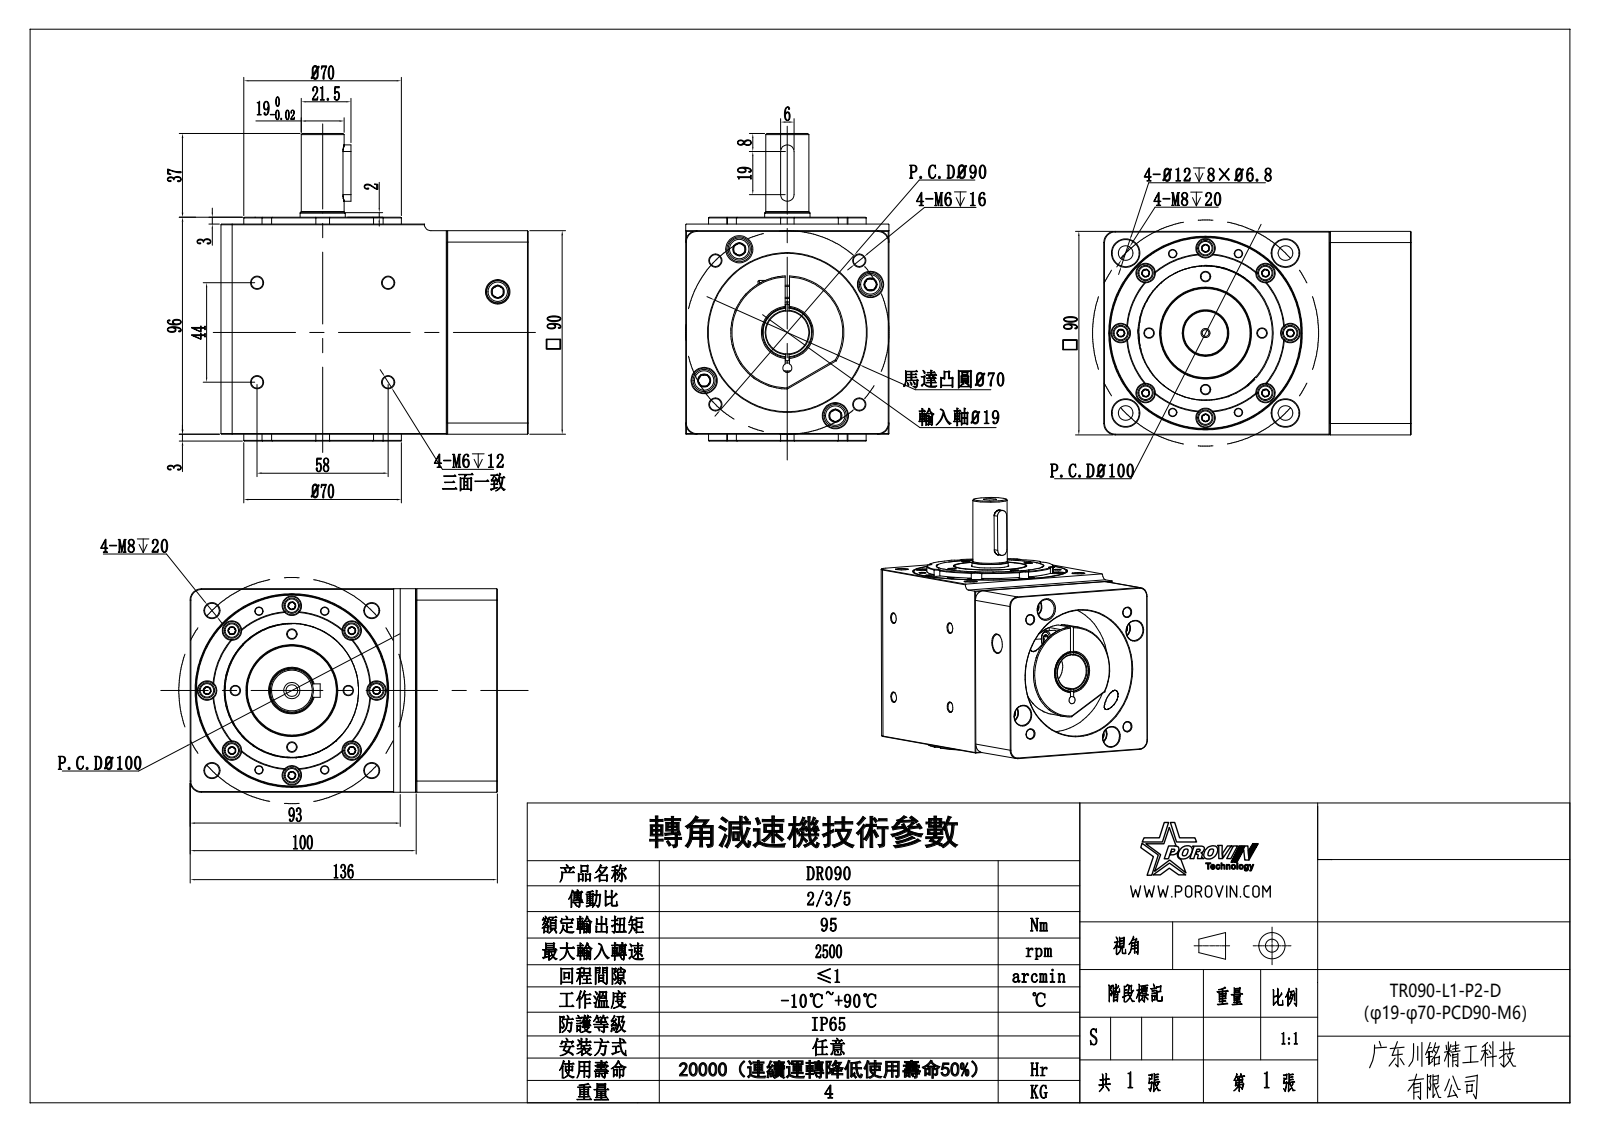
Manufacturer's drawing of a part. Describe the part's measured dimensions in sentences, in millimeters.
The part is named "DS90-2-19-41-70-90-m6_asm_stp_stp_stp". Its 3-D file was written by "SIEMENS PLM Software NX 10.0 (AP203_CONFIGURATION_CONTROLLED_3D_DESIGN_OF_MECHANICAL_PARTS_AND_ASSEMBLIES_MIM_LF)". It is 1 solid with 1052 faces: 398 planar, 261 cylindrical and 393 other. Overall it measures 136 by 136 by 90 millimeters. Its volume is 1 041 000 cubic millimeters and its surface area 109 747 square millimeters. Round holes: 14 of diameter 5.2, 9 of diameter 6.5, 8 of diameter 4.5, 8 of diameter 8, 5 of diameter 4, 4 of diameter 3.3, 4 of diameter 5, 4 of diameter 11, 4 of diameter 12, 2 of diameter 10.2, 1 of diameter 3, 1 of diameter 19. Round bosses or shafts: 8 of diameter 7, 8 of diameter 3.84, 5 of diameter 10, 5 of diameter 5.79, 1 of diameter 50, 1 of diameter 25, 1 of diameter 22, 1 of diameter 20. Partial cylindrical surfaces (rounded edges, fillets, slot ends): 6 of radius 5, 3 of radius 3, 1 of radius 5.75, 1 of radius 11, 1 of radius 24, 1 of radius 35, 1 of radius 44. The main face-to-face distances are 90, 3, 93, 96, 136, 6, 99, 25, 111, 5. The hole center spacings are 12.5, 14.74, 26.56, 28.7, 35.42, 36.85, 37.5, 41.95.
